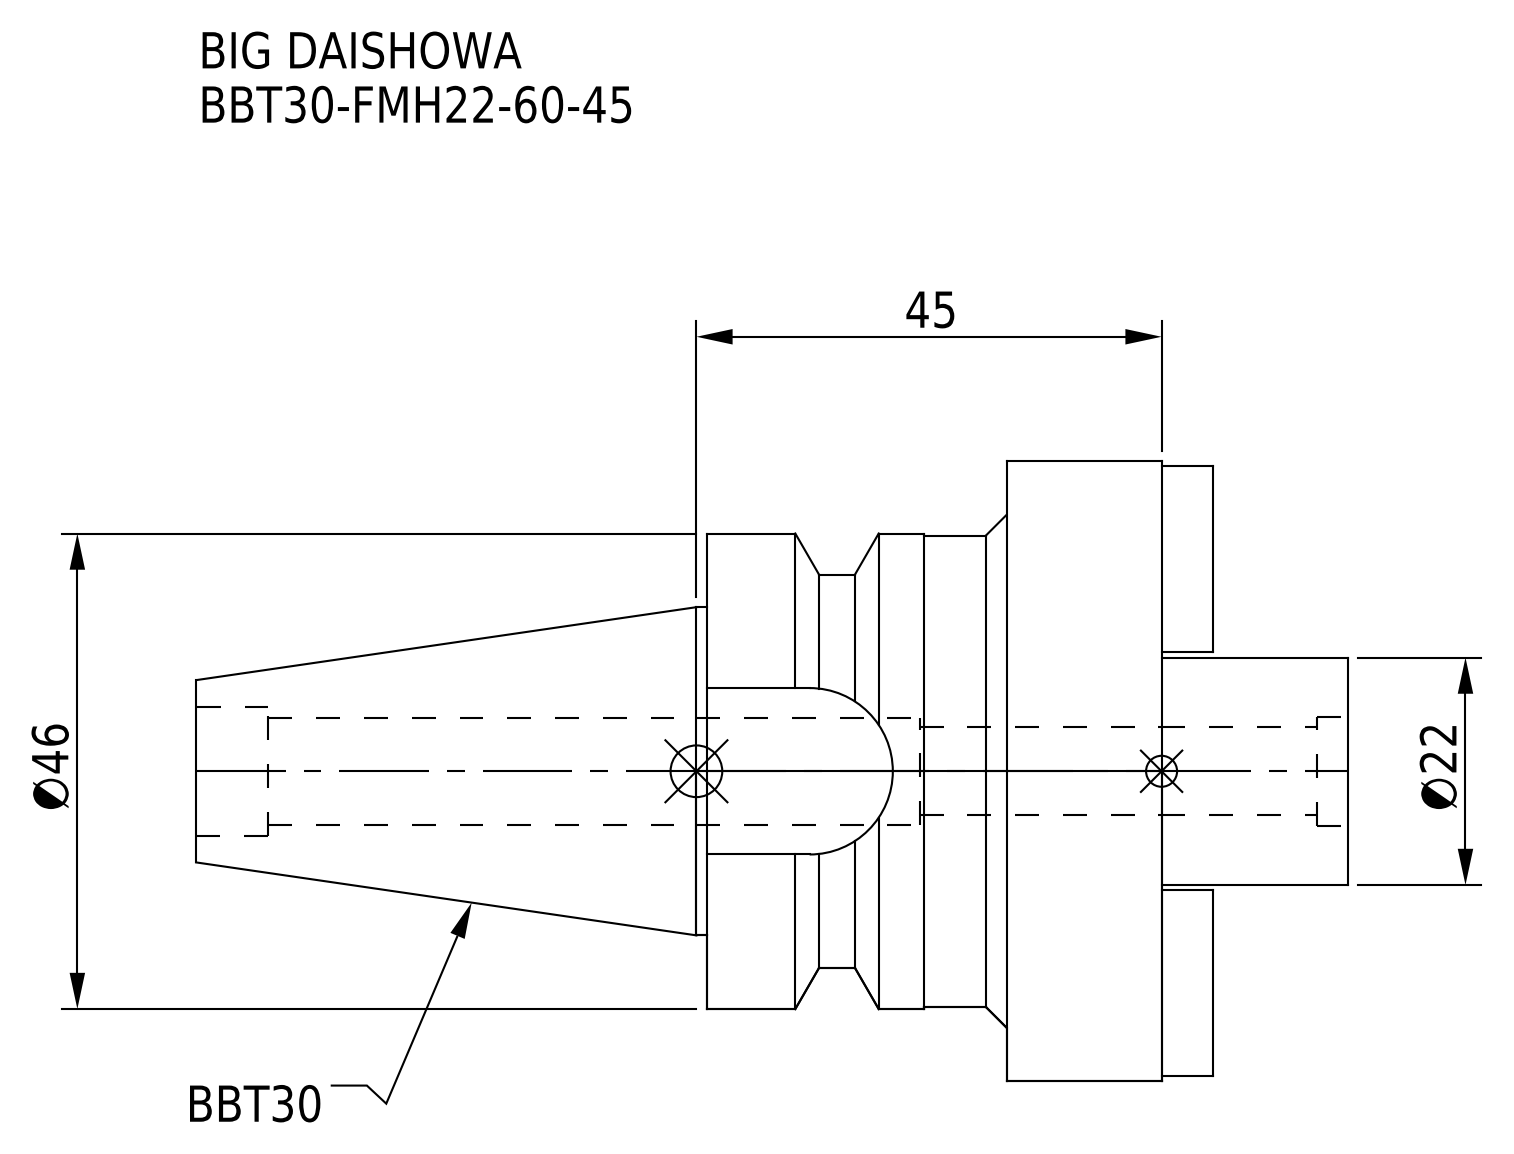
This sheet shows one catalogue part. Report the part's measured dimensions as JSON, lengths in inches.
{"part_name": "BBT30-FMH22-60-45", "step_written_by": "CREO PARAMETRIC BY PTC INC, 2016380 (AUTOMOTIVE_DESIGN)", "units": "inches", "bodies": {"solids": 1, "faces": 61, "planar": 25, "cylindrical": 28, "other": 8}, "overall_size": [4.386, 2.362, 2.362], "volume_in3": 6.688, "surface_area_in2": 33.44, "round_holes": [[0.335, 1], [0.409, 1], [0.413, 1], [0.492, 1]], "round_bosses_or_shafts": [[2.362, 1], [1.811, 1], [1.795, 1], [1.25, 1], [0.866, 1]], "partial_cylinders_radius": [[0.317, 1], [0.748, 1]], "face_to_face_distances": [0.591, 1.732, 1.142, 0.709, 0.197, 0.787, 1.929, 0.445, 0.839, 0.512]}
